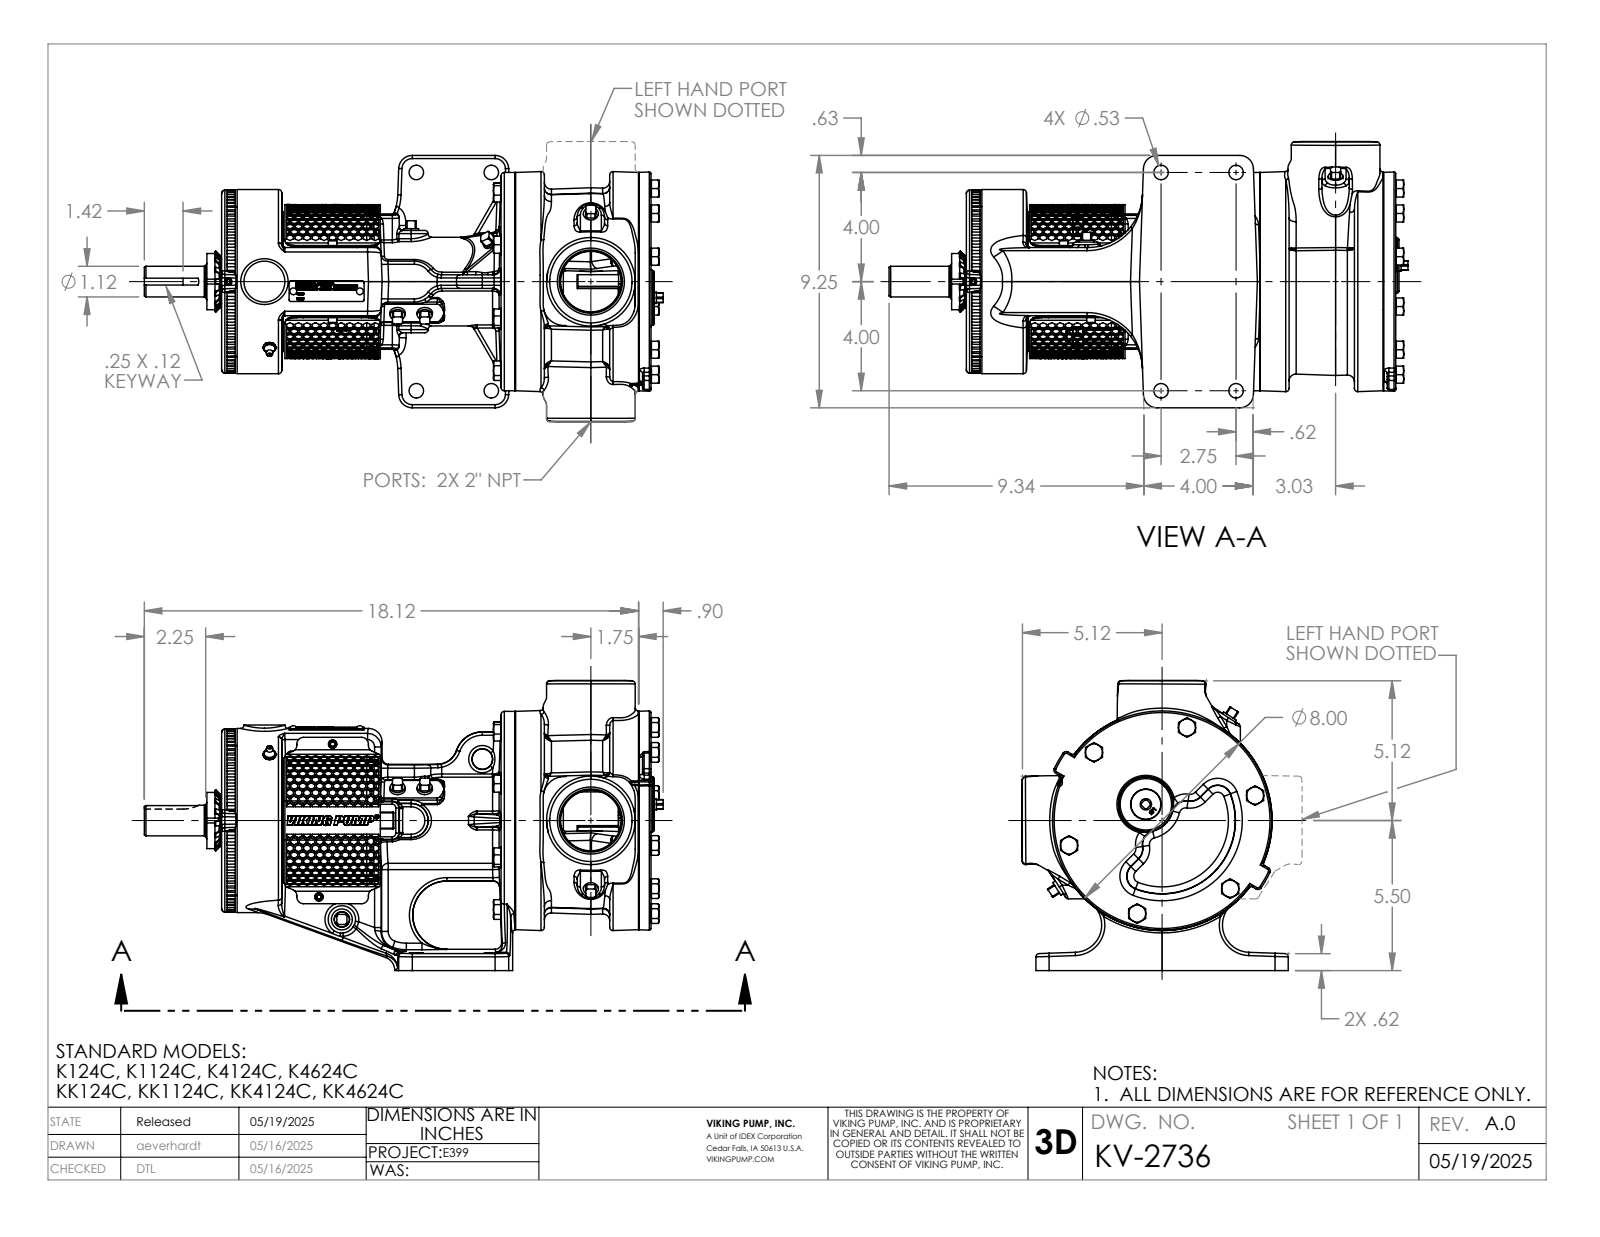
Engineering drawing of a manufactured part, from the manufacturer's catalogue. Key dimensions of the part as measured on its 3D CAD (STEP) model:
Part name (STEP PRODUCT): KV-2736
STEP written by: SolidWorks 2024 (AUTOMOTIVE_DESIGN)
Units: inches
Bodies: 1 solid, 3833 faces (1292 planar, 460 cylindrical, 2081 other)
Overall size (bounding box): 19.024 × 10.634 × 9.759
Volume: 456.5 in³ · Surface area: 885.2 in²
Round holes (diameter × count): ⌀0.78 ×8, ⌀0.197 ×6, ⌀0.25 ×6, ⌀0.531 ×4, ⌀0.159 ×2, ⌀0.313 ×2, ⌀0.257 ×1, ⌀0.453 ×1, ⌀1.122 ×1, ⌀1.38 ×1, ⌀1.387 ×1, ⌀1.695 ×1
Round bosses / shafts (diameter × count): ⌀0.625 ×9, ⌀0.625 ×5, ⌀0.437 ×3, ⌀0.312 ×3, ⌀8 ×1, ⌀6.75 ×1, ⌀5.497 ×1, ⌀3.25 ×1
Partial cylindrical surfaces — rounded edges, fillets, slot ends (radius × count): R0.12 ×77, R0.03 ×18, R0.24 ×18, R0.12 ×16, R0.25 ×13, R0.5 ×12, R0.06 ×10, R0.237 ×7
Main face-to-face distances: 10.425, 0.5, 5.319, 15.744, 0.569, 4.75, 15.175, 1, 1.5, 0.069
Hole centre spacings: 1.03, 3, 1.376, 2.385, 2.909, 3.531, 3.655, 3.799
